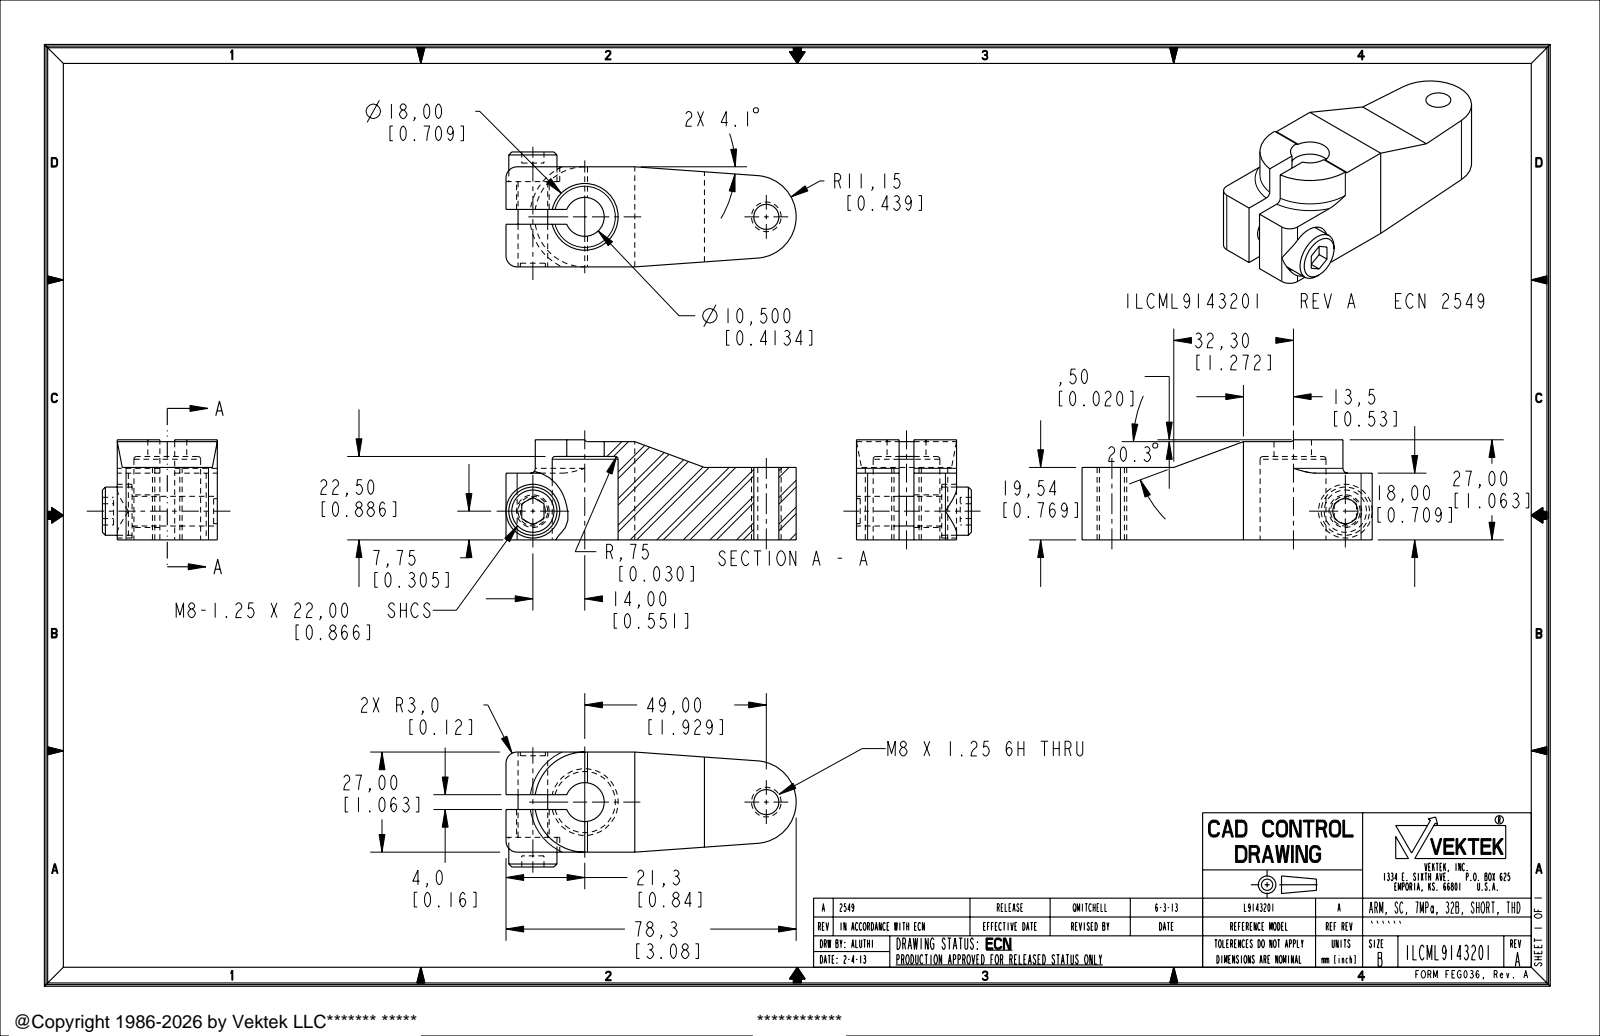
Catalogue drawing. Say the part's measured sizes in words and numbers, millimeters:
The part is named "ILCML9143201". Its 3-D file was written by "PRO/ENGINEER BY PARAMETRIC TECHNOLOGY CORPORATION, 2007460 (AUTOMOTIVE_DESIGN_CC2)". It is 1 solid with 59 faces: 28 planar, 26 cylindrical and 5 other. Overall it measures 78.3 by 31 by 27 millimeters. Its volume is 36 135 cubic millimeters and its surface area 11 780 square millimeters. Round holes: 2 of diameter 6.75, 1 of diameter 8.8, 1 of diameter 10.5, 1 of diameter 14.5, 1 of diameter 18. Round bosses or shafts: 2 of diameter 8, 1 of diameter 13. Partial cylindrical surfaces (rounded edges, fillets, slot ends): 2 of radius 3, 1 of radius 0.8, 1 of radius 11.15, 1 of radius 13.5. The main face-to-face distances are 27, 15.5, 11.5, 19.54, 4, 26.5, 6.96, 4.5, 18, 1.54. The hole center spacings are 49.
